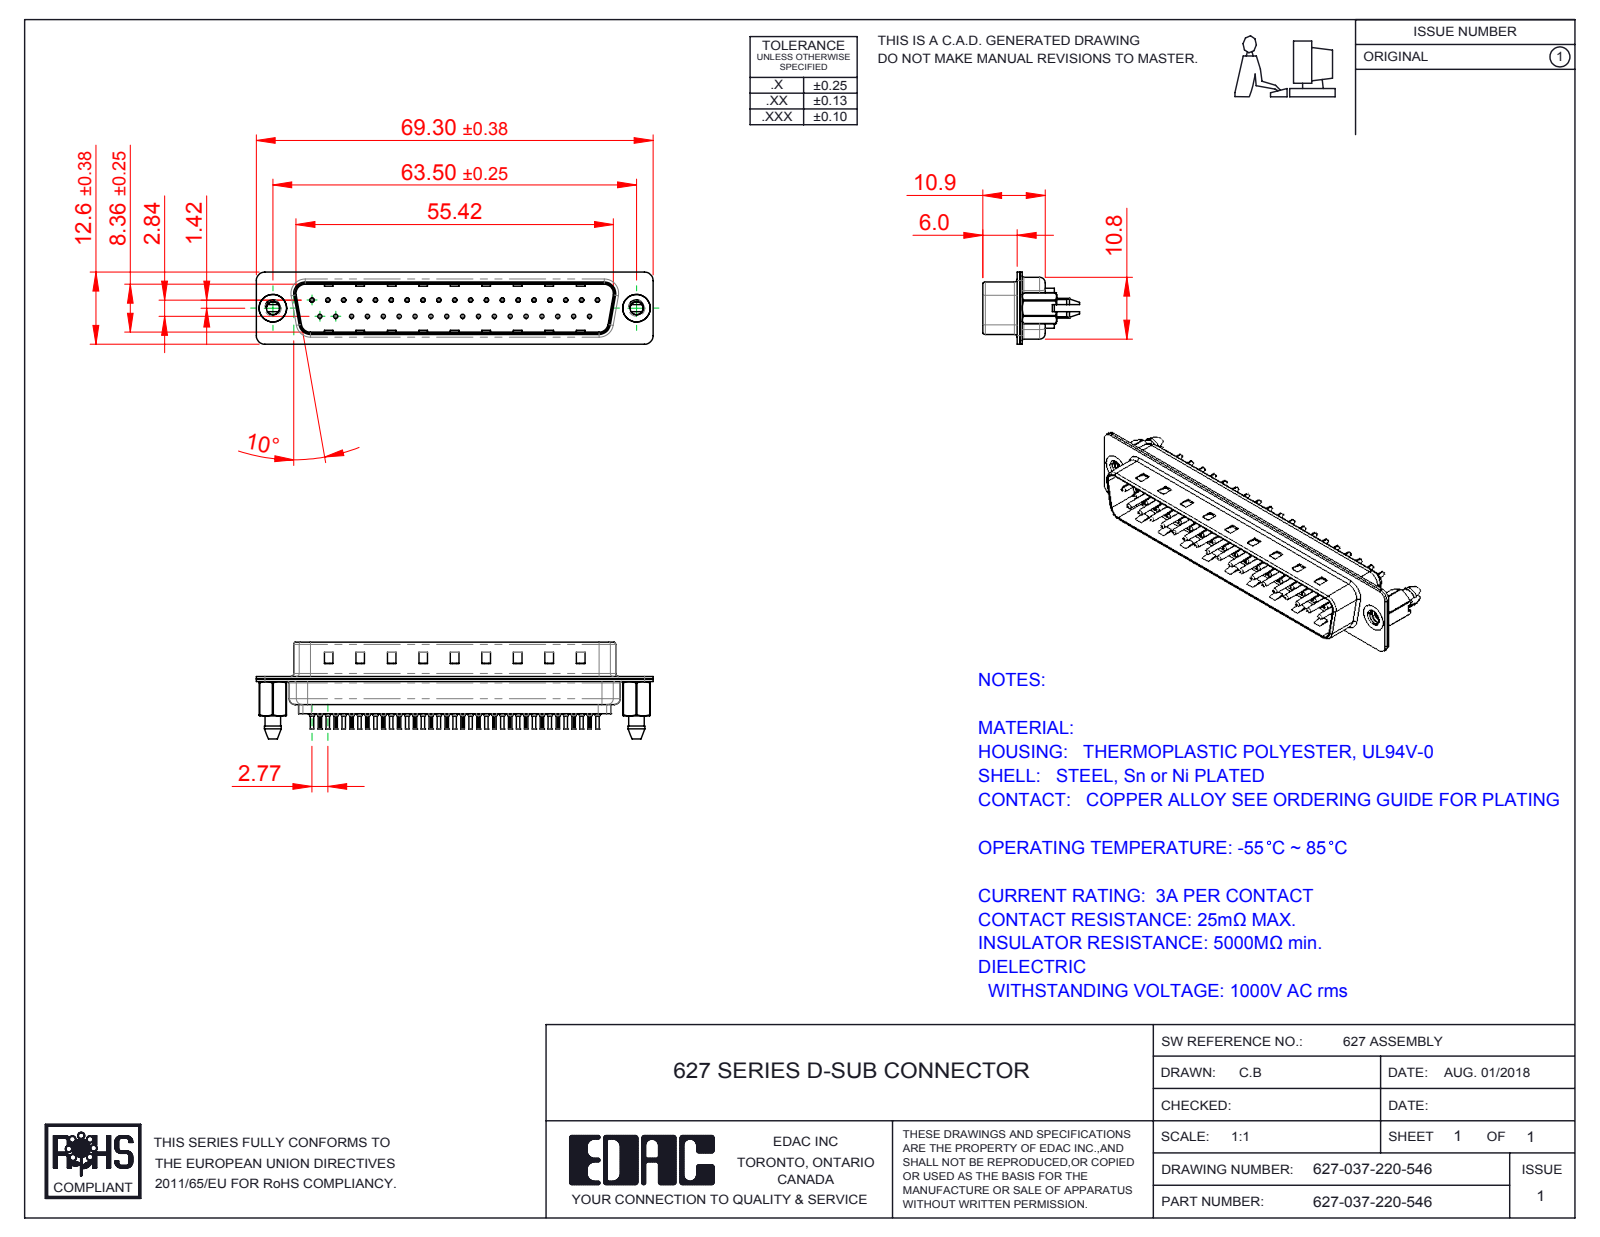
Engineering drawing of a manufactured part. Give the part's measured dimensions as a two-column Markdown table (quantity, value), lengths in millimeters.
| quantity | value |
| --- | --- |
| part name | 627 Contact Row 2_20L; 627 Shell Rear_37 Contacts; 627 Housing_37 LP; 627-037-220-546 (+3 more) |
| STEP written by | SolidWorks 2016 (CONFIG_CONTROL_DESIGN) |
| units | millimeters |
| bodies | 42 solids, 4112 faces (1123 planar, 1542 cylindrical, 1447 other) |
| overall size | 69.3 × 16.9 × 12.6 |
| volume | 3 797 mm³ |
| surface area | 10 748 mm² |
| round holes (diameter × count) | 0.2 × 37, 0.35 × 37, 1.1 × 37, 1.6 × 37, 2.26 × 2, 4 × 2, 4.8 × 2 |
| round bosses / shafts (diameter × count) | 2 × 37, 1.5 × 37, 0.75 × 37, 0.6 × 37, 4.9 × 2 |
| partial cylindrical surfaces (radius × count) | 0.1 × 74, 1.5 × 18, 2 × 12, 1.6 × 10, 0.5 × 8, 0.25 × 4, 0.6 × 4, 0.65 × 4 |
| main face-to-face distances | 0.4, 0.82, 9.58, 0.45, 8.76, 1.5, 0.9, 1.4, 6.5, 6.05 |
| hole center spacings | 3.16, 2.77, 5.54, 8.31, 5.04, 10.1, 11.08, 12.78 |
